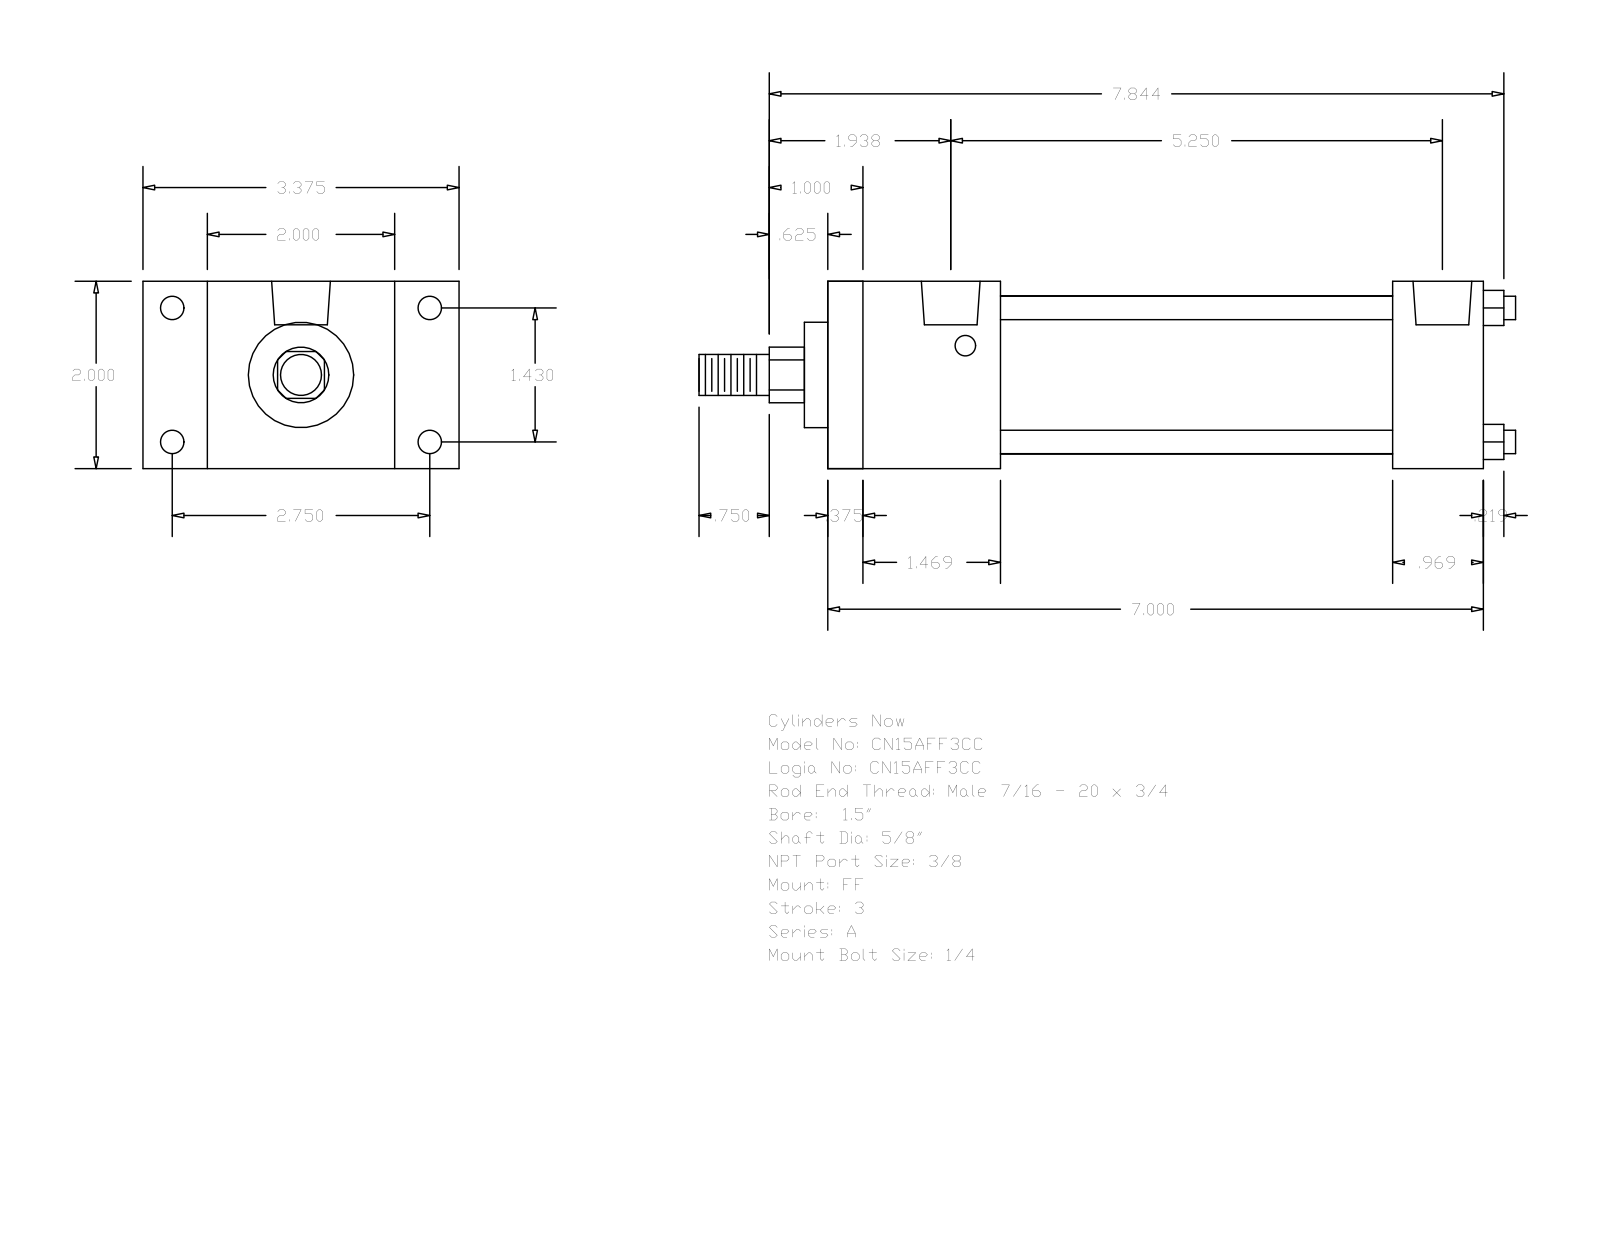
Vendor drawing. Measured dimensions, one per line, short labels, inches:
name: A_FF__0150_0.625
written by: GSSL Pune (CONFIG_CONTROL_DESIGN)
unit: in
bodies: 0 solids, 92 faces (64 planar, 28 cylindrical, 0 other)
size: 8.719 × 3.375 × 2
holes: 4× ⌀0.219, 4× ⌀0.25, 2× ⌀0.627
bosses: 4× ⌀0.25, 1× ⌀1.69, 1× ⌀1.125, 1× ⌀0.625, 1× ⌀0.437
rounds: 1× R0.297
face distances: 2, 7, 0.375, 6.625, 1.844, 6.031, 1.469, 5.656, 4.187, 5.156
hole spacings: 0.156, 1.43, 2.75, 3.099, 4.937, 5.094, 5.25
